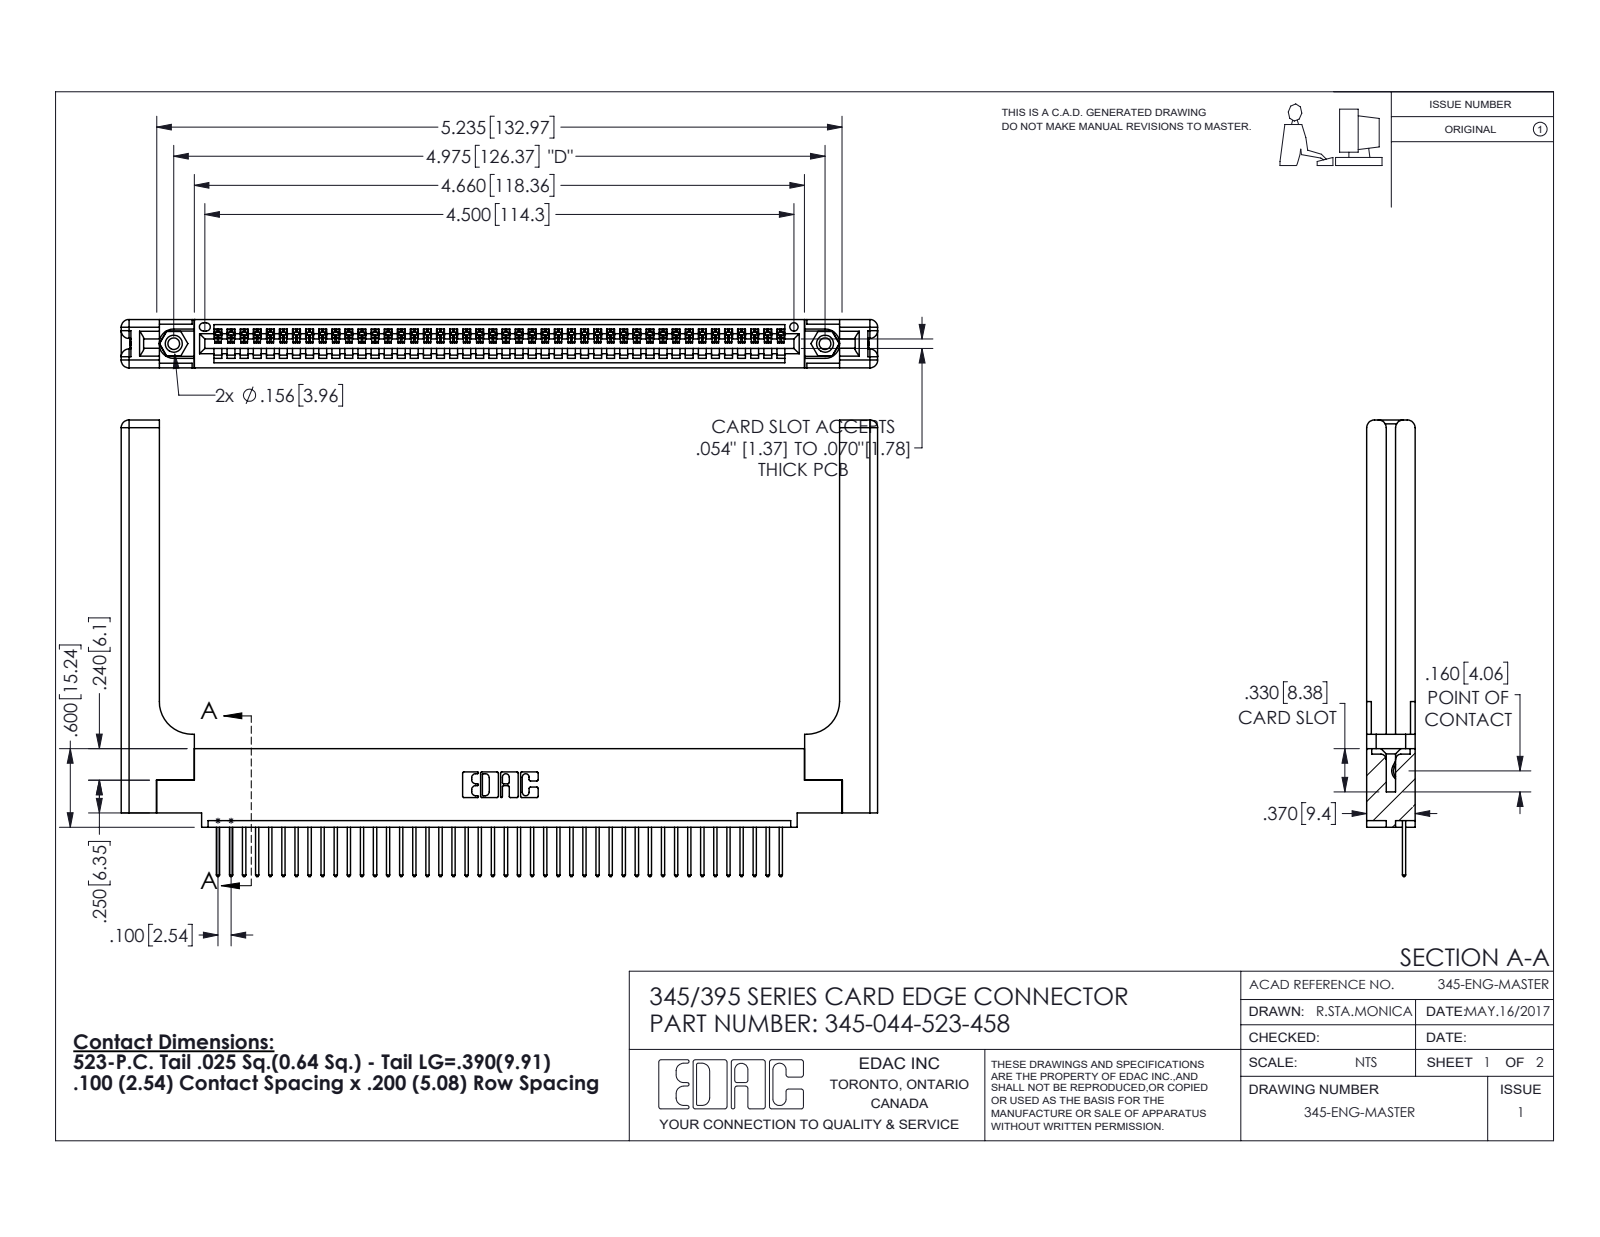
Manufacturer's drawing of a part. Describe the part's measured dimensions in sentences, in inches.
The part is named "345-044-523-458; 345-220-058_345-220-058; 345-250-001_345-250-001-102; 345-292-001_345-293-123 (+1 more)". Its 3-D file was written by "SolidWorks 2016 (CONFIG_CONTROL_DESIGN)". It is 49 solids with 2938 faces: 1992 planar, 886 cylindrical and 60 other. Overall it measures 5.779 by 3.487 by 0.37 inches. Its volume is 1.365 cubic inches and its surface area 37.03 square inches. Round holes: 2 of diameter 0.089, 2 of diameter 0.125, 2 of diameter 0.156, 1 of diameter 0.064. Round bosses or shafts: 2 of diameter 0.155. Partial cylindrical surfaces (rounded edges, fillets, slot ends): 88 of radius 0.006, 88 of radius 0.01, 22 of radius 0.01, 16 of radius 0.06, 6 of radius 0.007, 6 of radius 0.031, 3 of radius 0.026, 2 of radius 0.03. The main face-to-face distances are 0.072, 0.37, 0.298, 0.098, 0.272, 0.025, 0.2, 0.225, 0.148, 0.15. The hole center spacings are 0.27, 4.739, 4.975.
